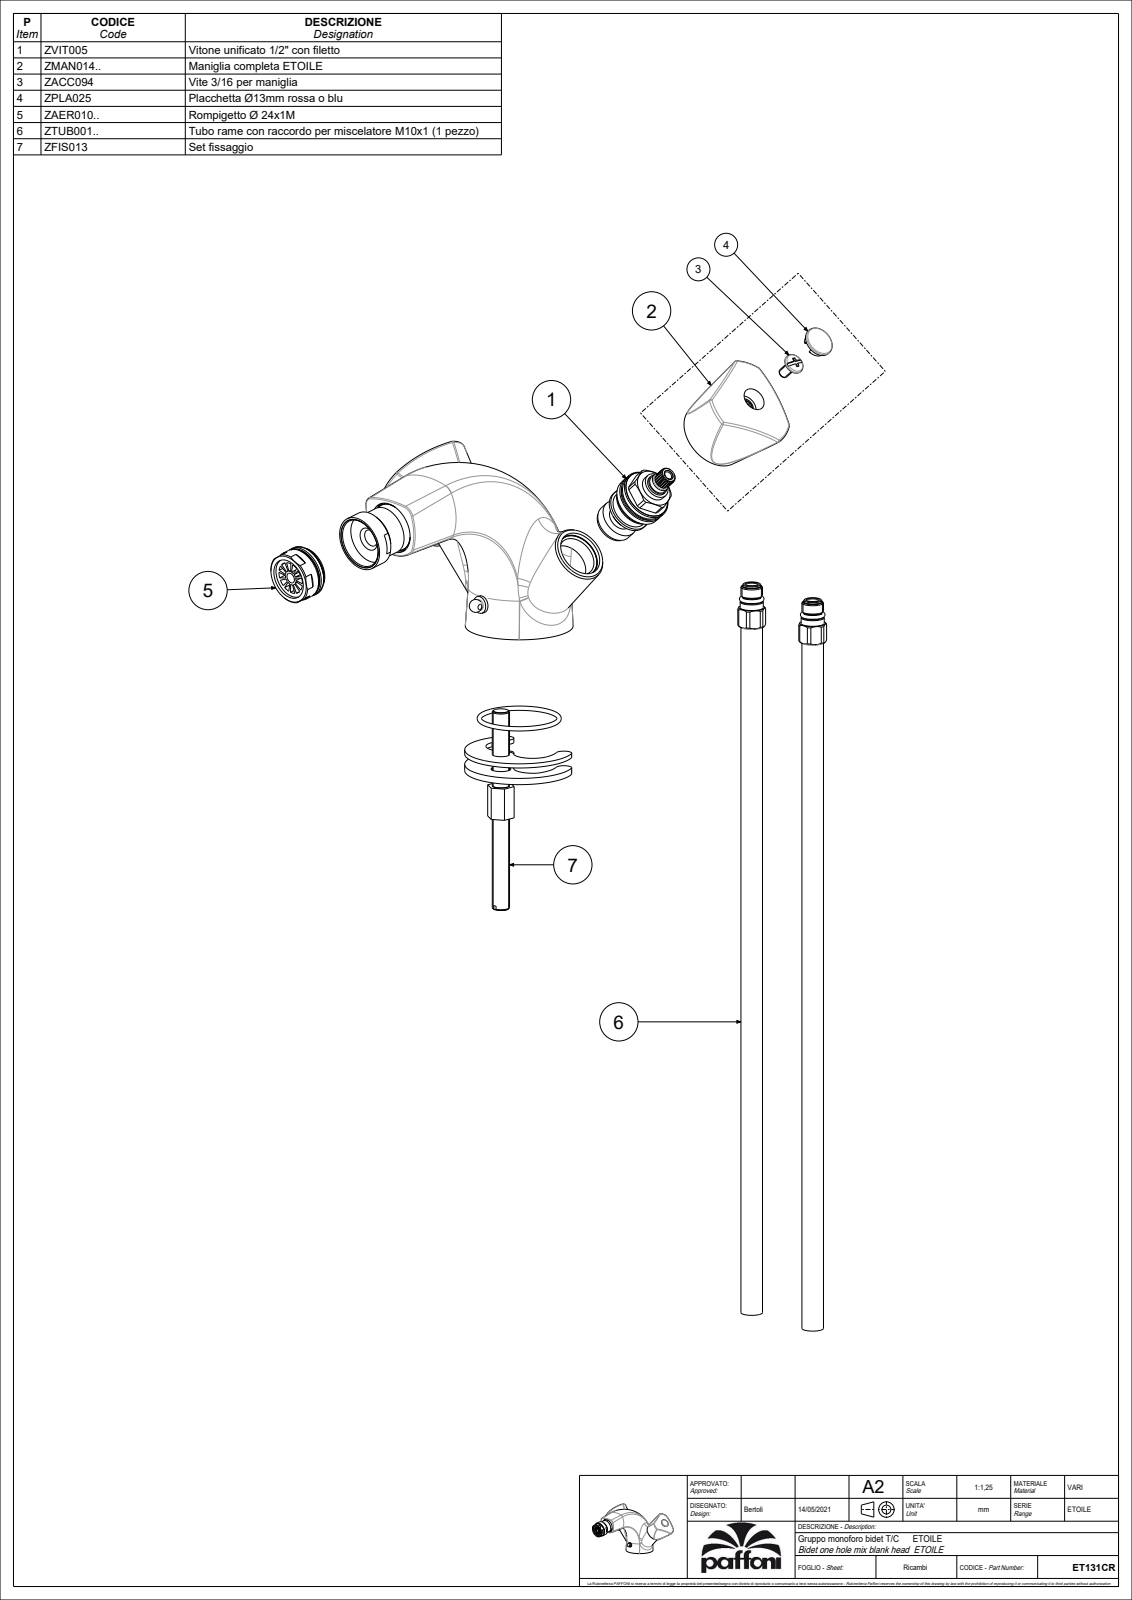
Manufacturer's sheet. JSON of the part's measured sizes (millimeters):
{"part_name": "ET131CR", "step_written_by": "CREO PARAMETRIC BY PTC INC, 2020044 (CONFIG_CONTROL_DESIGN)", "units": "millimeters", "bodies": {"solids": 1, "faces": 591, "planar": 151, "cylindrical": 148, "other": 292}, "overall_size": [154.04, 138.85, 85.43], "volume_mm3": 142377, "surface_area_mm2": 72437, "round_holes": [[8, 3], [19, 3], [9, 2], [11, 2], [29.6, 2], [2.5, 1], [4.8, 1], [6, 1], [6.8, 1], [15, 1], [15.5, 1], [16, 1]], "round_bosses_or_shafts": [[24, 3], [22.5, 3], [18.6, 2], [17.3, 2], [14, 2], [12.5, 2], [11.5, 2], [9, 2]], "partial_cylinders_radius": [[1, 4], [3, 2], [5, 2], [8, 2], [10, 2], [13, 2], [13.5, 2], [3.4, 1]], "face_to_face_distances": [6, 23, 40.81, 11, 1.5, 29, 15, 3, 9, 17], "hole_center_spacings": [7.5, 12.5, 14.15, 10, 12, 15, 22]}
